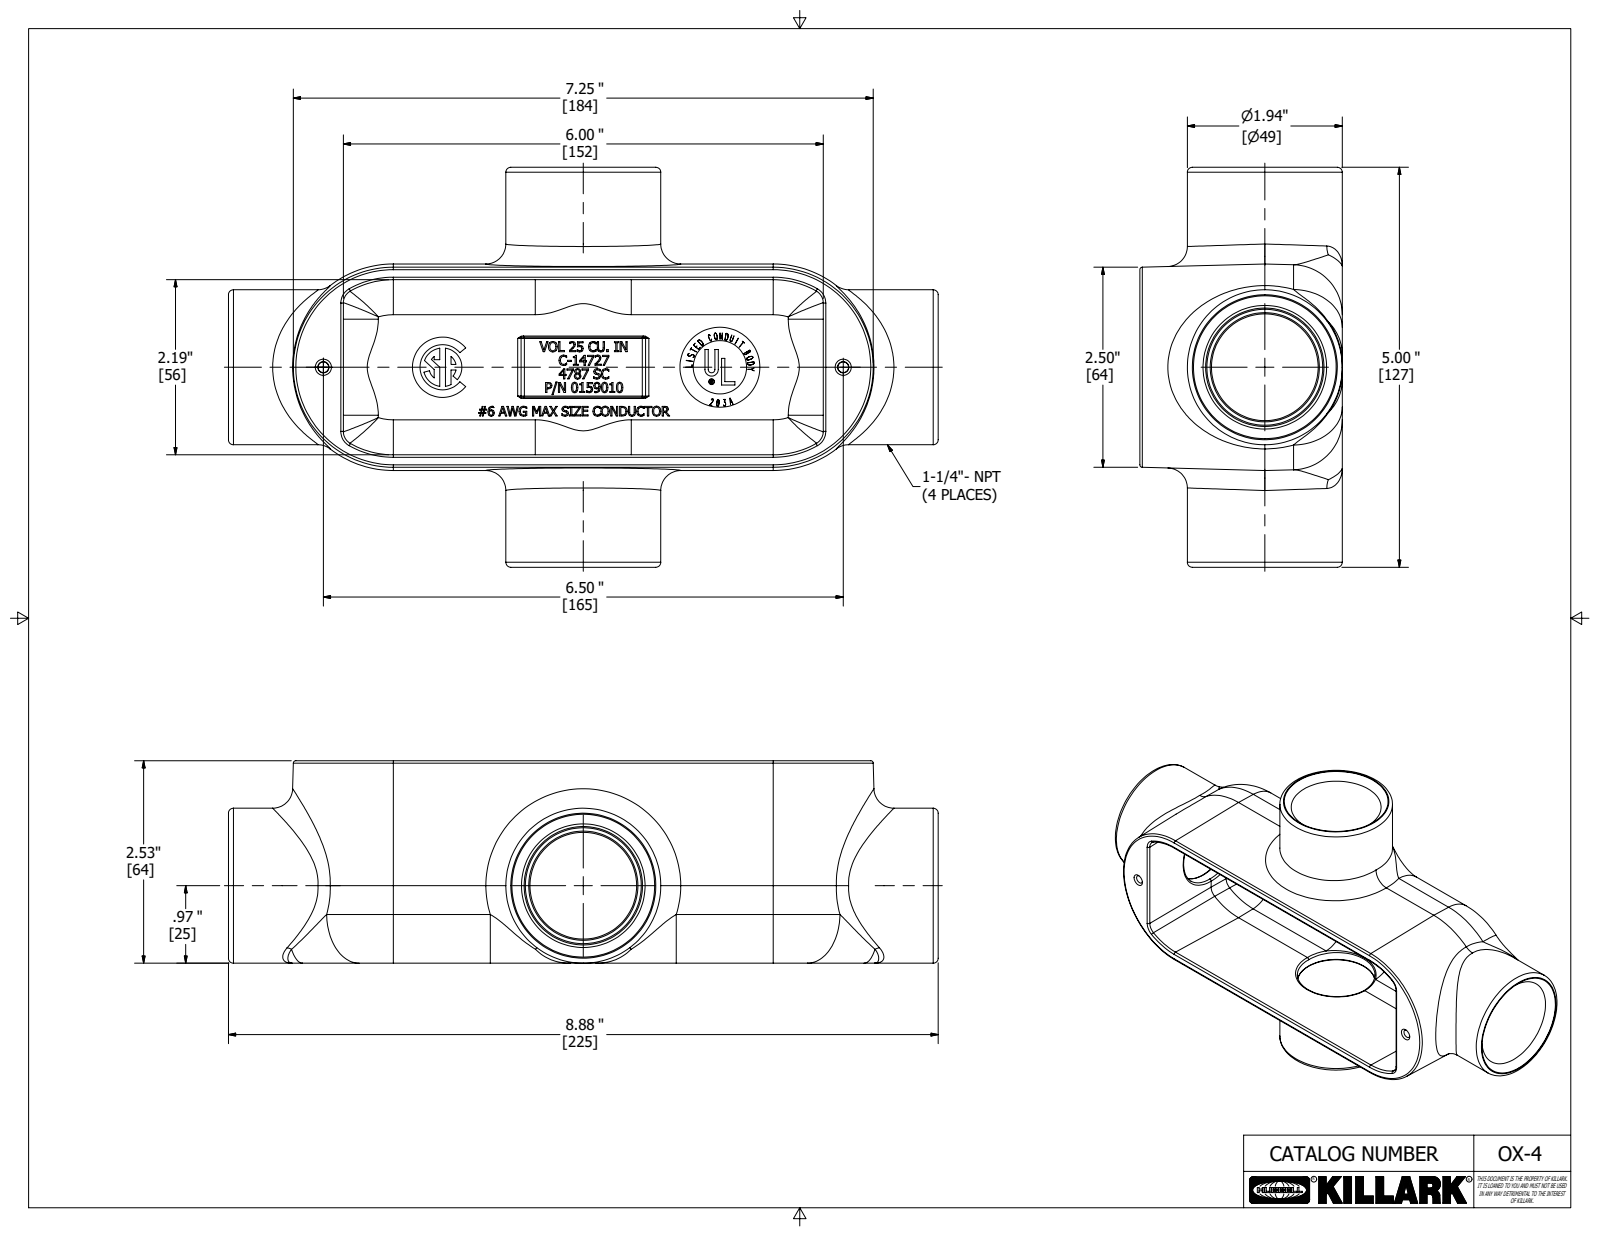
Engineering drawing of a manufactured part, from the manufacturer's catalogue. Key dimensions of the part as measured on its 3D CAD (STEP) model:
Part name (STEP PRODUCT): 14727-1
STEP written by: Autodesk Inventor 2018 (AUTOMOTIVE_DESIGN)
Units: inches
Bodies: 1 solid, 1715 faces (1148 planar, 58 cylindrical, 509 other)
Overall size (bounding box): 8.875 × 5 × 2.531
Volume: 14.28 in³ · Surface area: 148 in²
Round holes (diameter × count): ⌀1.334 ×2, ⌀0.063 ×1, ⌀0.667 ×1
Round bosses / shafts (diameter × count): ⌀1.937 ×2, ⌀1 ×1, ⌀0.071 ×1
Partial cylindrical surfaces — rounded edges, fillets, slot ends (radius × count): R0.062 ×12, R0.031 ×6, R0.015 ×4, R0.469 ×4, R0.625 ×2, R0.042 ×1, R0.083 ×1, R0.171 ×1
Main face-to-face distances: 0.156, 2.425, 2.531, 2.375, 2.269, 0.031, 2.581, 0.187, 2.344, 0.125
Hole centre spacings: 0.209
